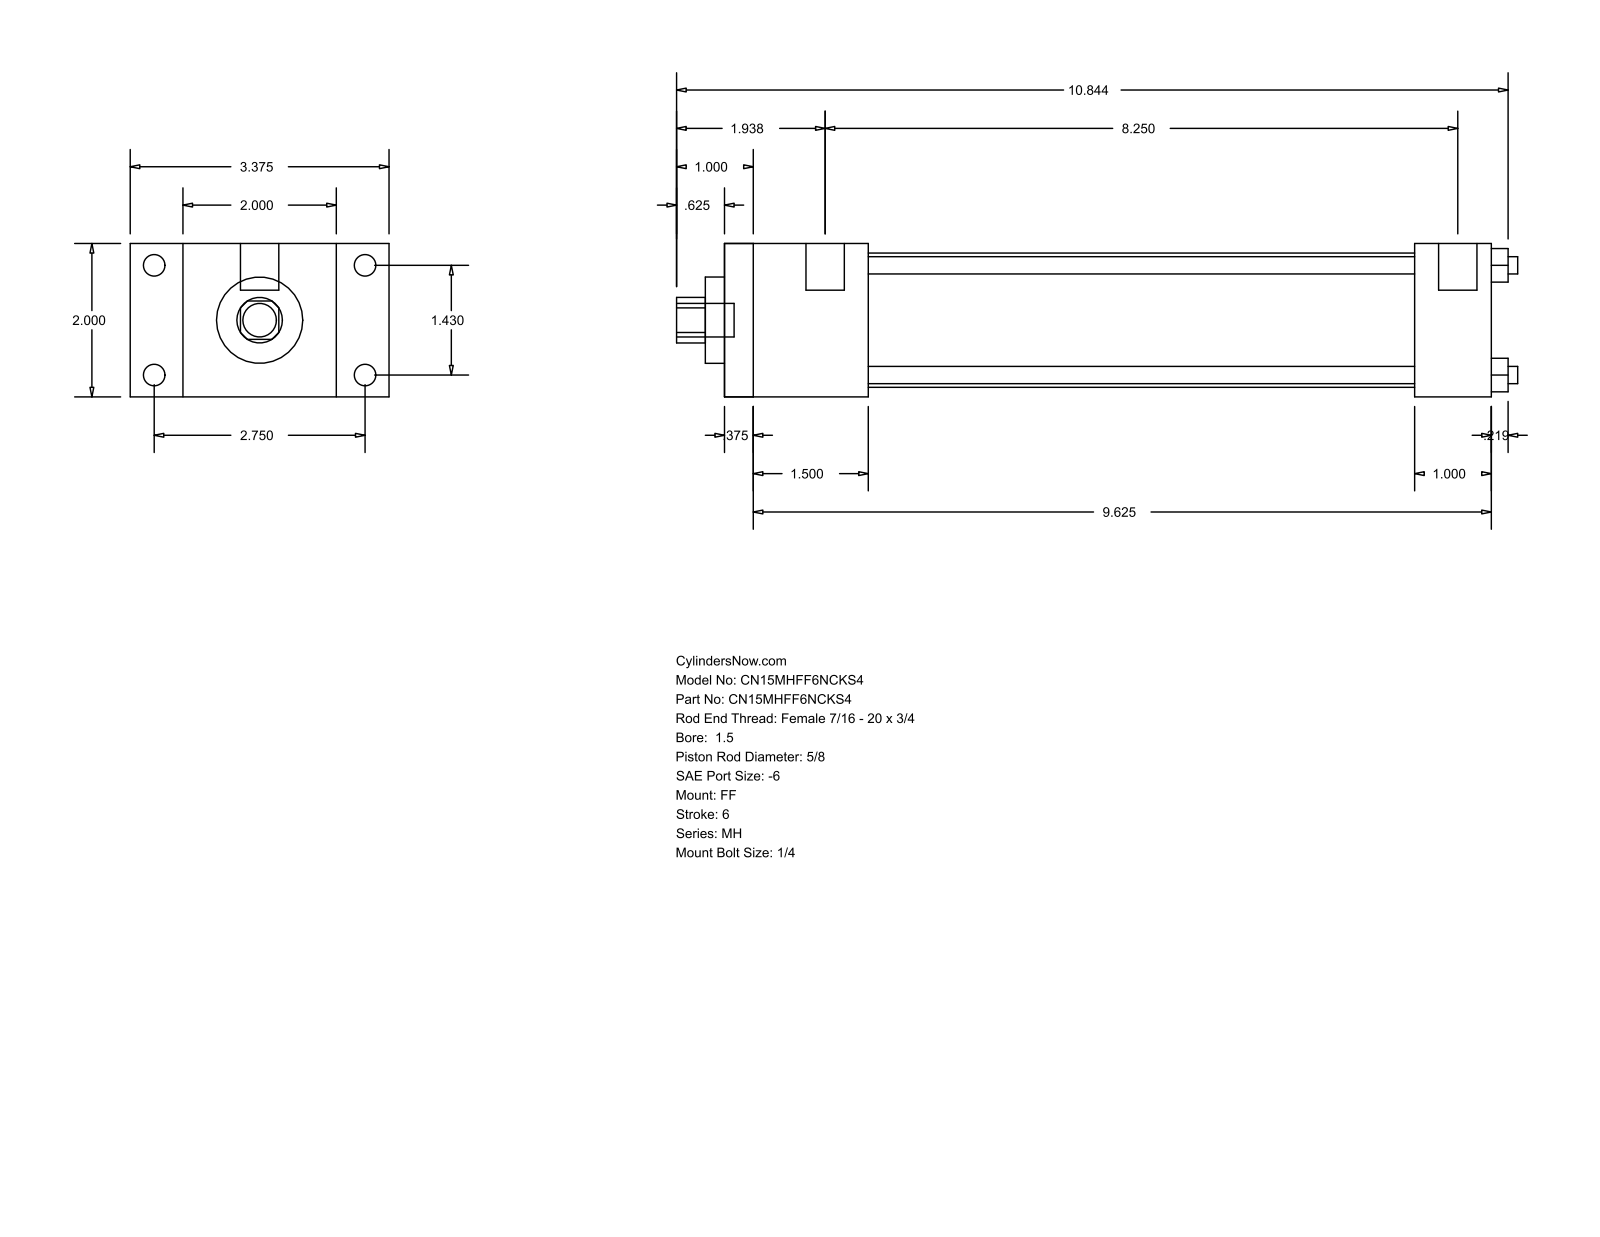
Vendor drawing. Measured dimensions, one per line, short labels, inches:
name: MH_FF__0150_0.625
written by: GSSL Pune (CONFIG_CONTROL_DESIGN)
unit: in
bodies: 0 solids, 92 faces (64 planar, 28 cylindrical, 0 other)
size: 10.969 × 3.375 × 2
holes: 4× ⌀0.225, 1× ⌀0.625, 1× ⌀1.125, 1× ⌀1.75
bosses: 4× ⌀0.281, 4× ⌀0.219, 2× ⌀0.5, 1× ⌀0.437
rounds: 1× R0.297
face distances: 2, 10, 0.375, 9.625, 0.687, 2.687, 1.875, 1.5, 8.125, 9
hole spacings: 1.011, 1.43, 2.022
